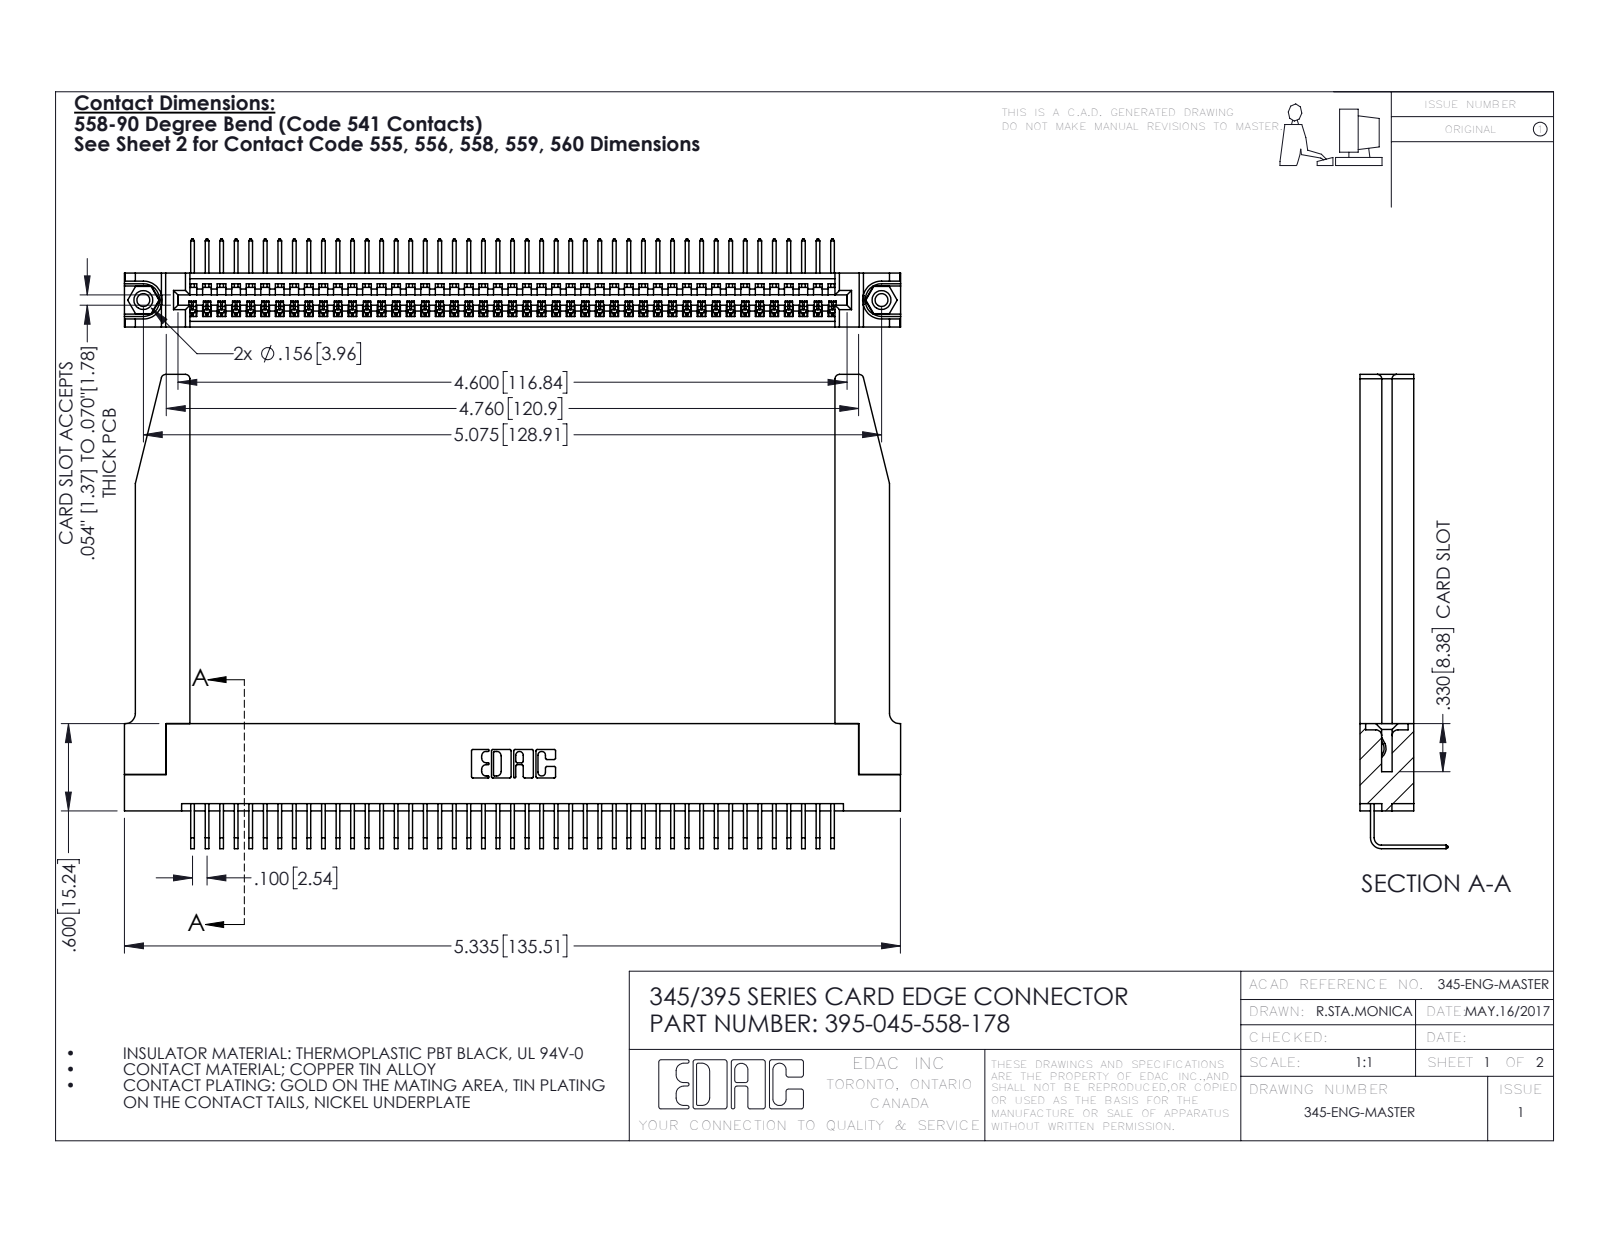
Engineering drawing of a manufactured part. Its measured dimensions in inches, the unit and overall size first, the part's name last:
Units: inches
Overall size (bounding box): 5.336 × 3.259 × 0.605
Round holes (diameter × count): ⌀0.089 ×2, ⌀0.125 ×2, ⌀0.156 ×2, ⌀0.064 ×1
Round bosses / shafts (diameter × count): ⌀0.155 ×2
Partial cylindrical surfaces — rounded edges, fillets, slot ends (radius × count): R0.006 ×90, R0.01 ×22, R0.03 ×8, R0.007 ×6, R0.031 ×6, R0.026 ×3, R0.031 ×2, R0.04 ×2
Main face-to-face distances: 0.37, 0.072, 0.298, 0.2, 0.098, 0.272, 0.025, 0.225, 0.148, 0.15
Hole centre spacings: 0.27, 4.839, 5.075
Volume: 1.27 in³ · Surface area: 38.92 in²
Bodies: 50 solids, 3060 faces (2112 planar, 896 cylindrical, 52 other)
Part name (STEP PRODUCT): 345 Part_Flush Mounting Lugs - 0.156 Dia-TH; 345-250-001_345-250-001-102; 345-220-078_345-220-078; 345-292-001_558 Tail - 2 (+1 more)
STEP written by: SolidWorks 2016 (CONFIG_CONTROL_DESIGN)
